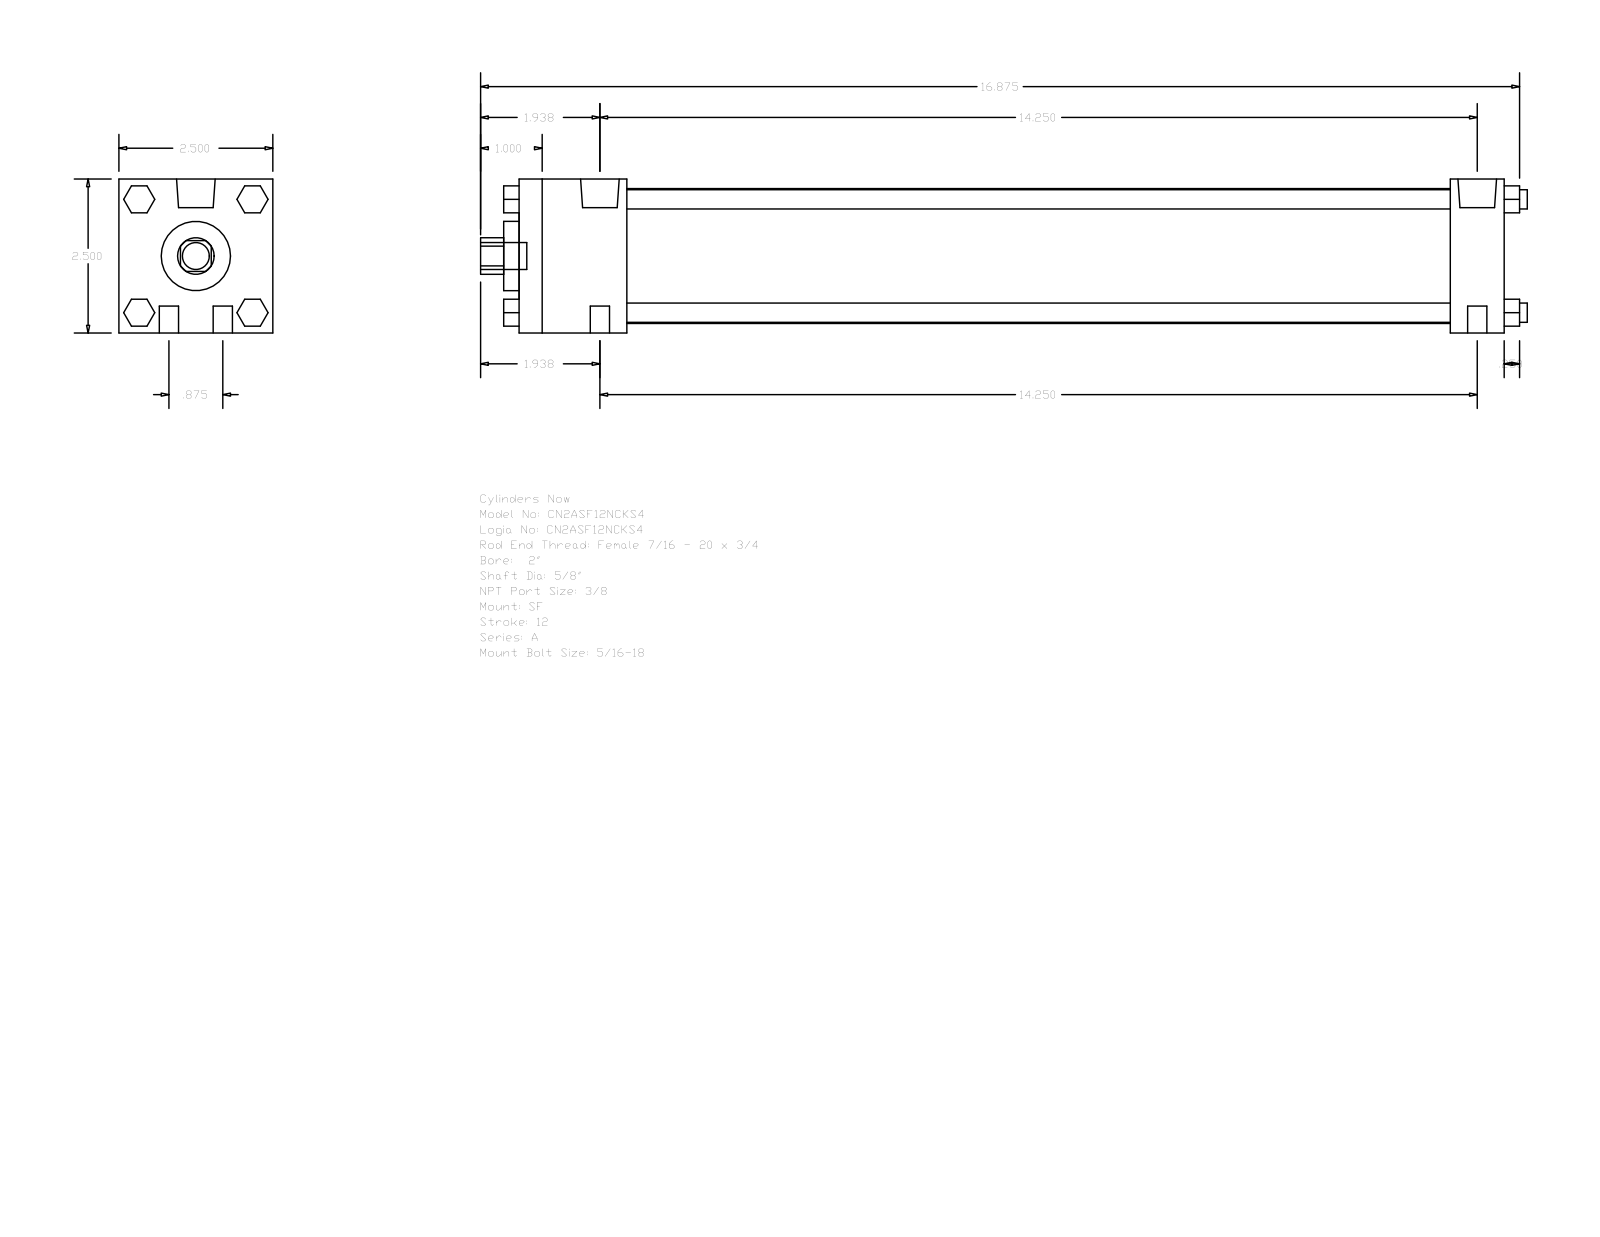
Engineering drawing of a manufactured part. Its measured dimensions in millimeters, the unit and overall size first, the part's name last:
Units: millimetres
Overall size (bounding box): 431.8 × 63.5 × 63.5
Round holes (diameter × count): ⌀15.88 ×1, ⌀28.57 ×1, ⌀55.63 ×1
Round bosses / shafts (diameter × count): ⌀7.94 ×8, ⌀15.93 ×2, ⌀5.56 ×2, ⌀11.11 ×1
Partial cylindrical surfaces — rounded edges, fillets, slot ends (radius × count): R7.54 ×1
Main face-to-face distances: 63.5, 406.39, 384.17, 22.22, 44.45, 339.72, 361.94, 6.35, 412.74, 50.8
Bodies: 0 solids, 124 faces (94 planar, 30 cylindrical, 0 other)
Part name (STEP PRODUCT): A_SF__0200_0.625
STEP written by: GSSL Pune (CONFIG_CONTROL_DESIGN)
